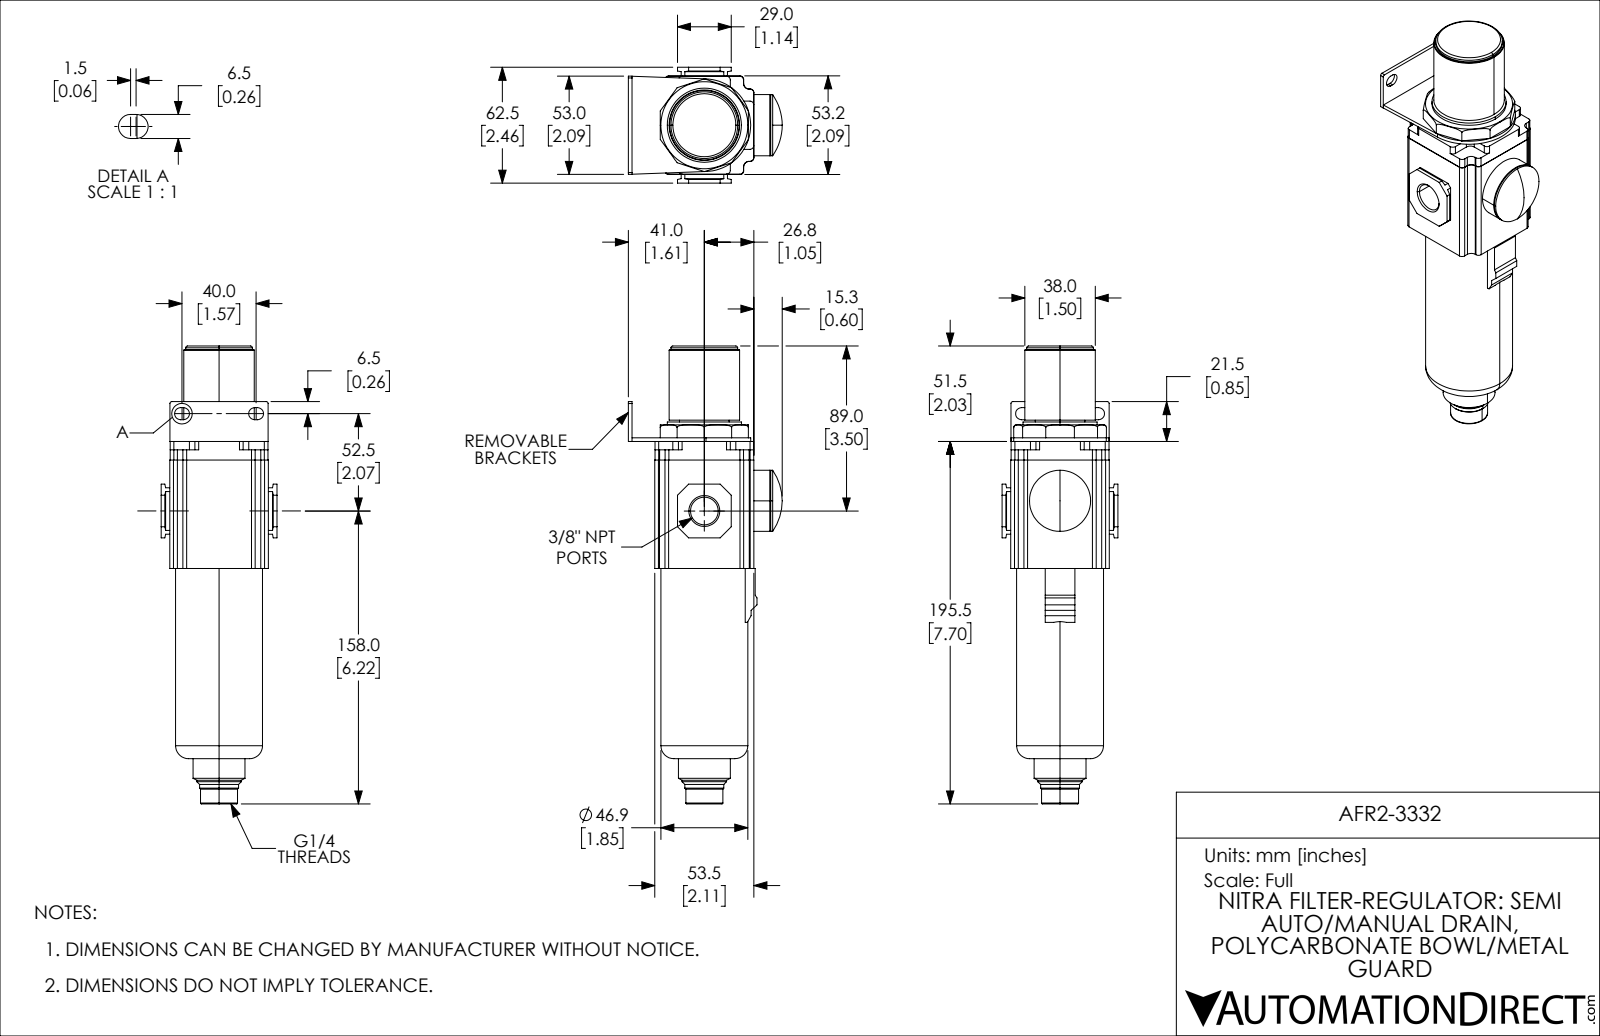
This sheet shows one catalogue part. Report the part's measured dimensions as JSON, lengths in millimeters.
{"part_name": "AFR2-3332", "step_written_by": "SolidWorks 2019 (CONFIG_CONTROL_DESIGN)", "units": "millimeters", "bodies": {"solids": 1, "faces": 221, "planar": 124, "cylindrical": 71, "other": 26}, "overall_size": [247, 83.03, 62.5], "volume_mm3": 449570, "surface_area_mm2": 52239, "round_holes": [[11.45, 1], [14.95, 1]], "round_bosses_or_shafts": [[46.9, 1], [40, 1], [38, 1], [36, 1], [33, 1], [28, 1], [26.78, 1], [24, 1]], "partial_cylinders_radius": [[2, 24], [3, 12], [3.25, 4], [1, 2], [25, 1]], "face_to_face_distances": [2, 53.2, 53.5, 14.25, 4.65, 57.85, 12.25, 67.75, 51.5, 49.5]}
